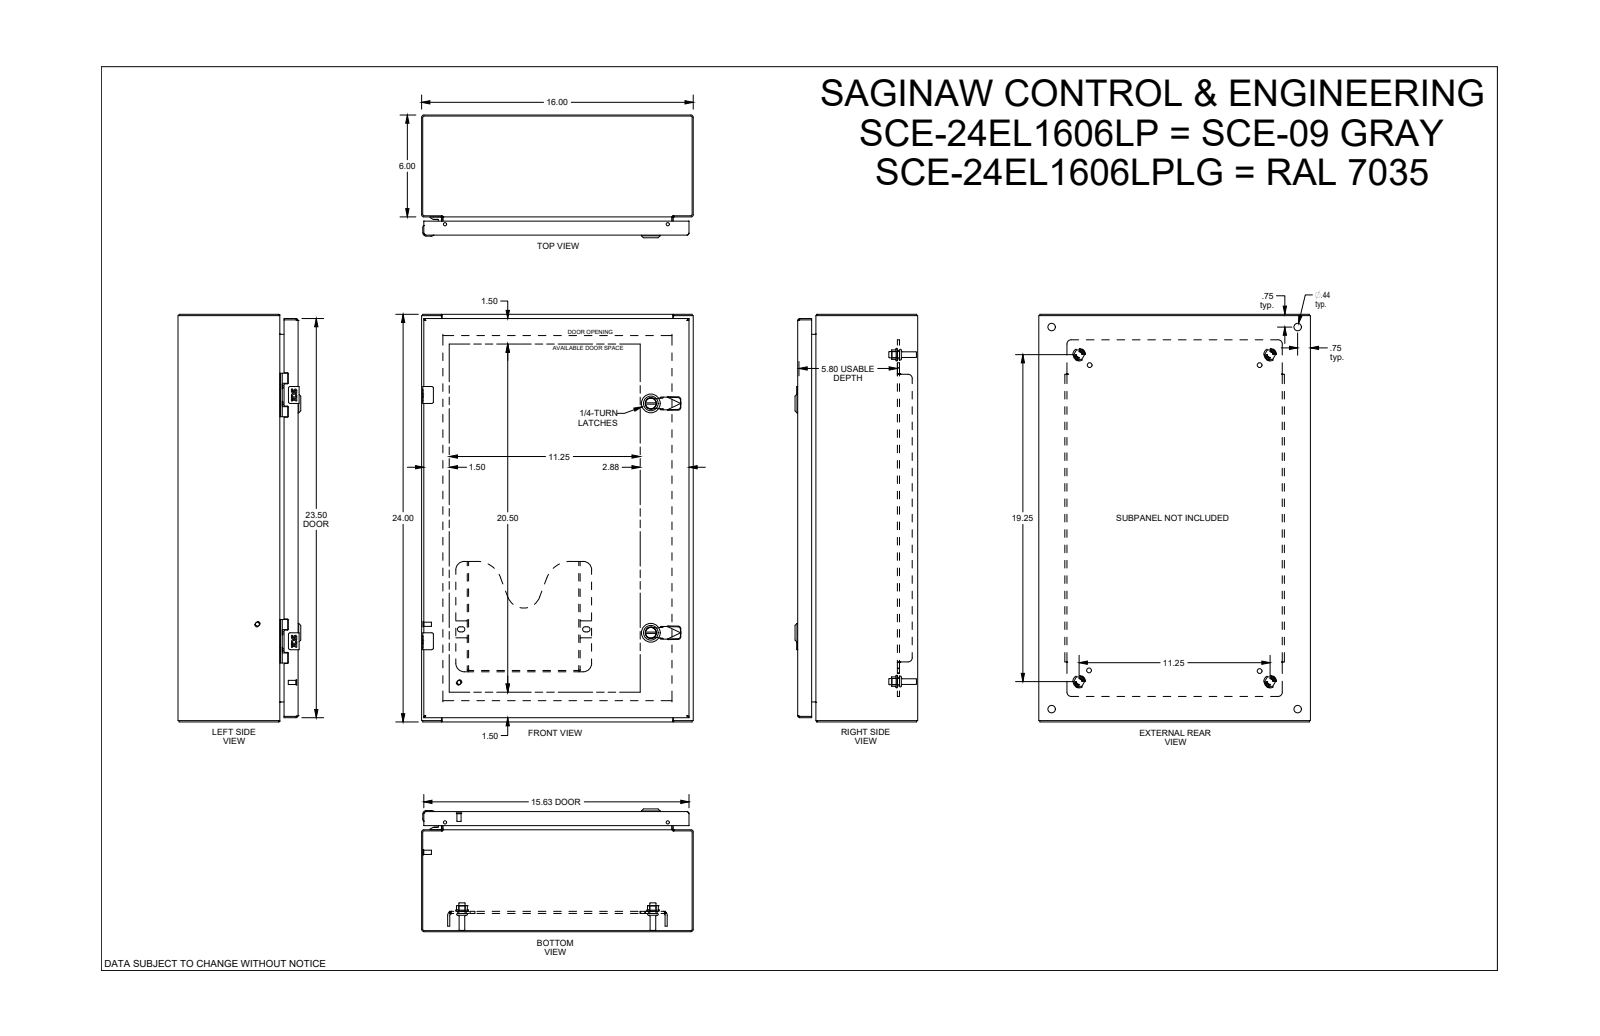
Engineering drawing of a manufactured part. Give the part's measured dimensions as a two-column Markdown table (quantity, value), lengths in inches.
| quantity | value |
| --- | --- |
| part name | SCE-24EL1606LP |
| STEP written by | SolidWorks 2021 (AUTOMOTIVE_DESIGN) |
| units | inches |
| bodies | 45 solids, 2787 faces (1089 planar, 840 cylindrical, 858 other) |
| overall size | 24 × 16 × 7.23 |
| volume | 156.9 in³ |
| surface area | 3 771 in² |
| round holes (diameter × count) | 0.172 × 4, 0.205 × 4, 0.244 × 4, 0.266 × 4, 0.281 × 4, 0.367 × 4, 0.375 × 4, 0.437 × 4, 0.5 × 4, 0.04 × 2, 0.188 × 2, 0.197 × 2 |
| round bosses / shafts (diameter × count) | 0.17 × 6, 0.366 × 4, 0.332 × 4, 0.25 × 4, 0.248 × 4, 0.24 × 4, 0.196 × 3, 1.102 × 2 |
| partial cylindrical surfaces (radius × count) | 0.012 × 56, 0.01 × 28, 0.015 × 24, 0.02 × 20, 0.04 × 17, 0.06 × 13, 0.029 × 12, 0.1 × 12 |
| main face-to-face distances | 0.075, 0.06, 7.073, 6.998, 7.013, 6.938, 1, 0.125, 15.925, 1.2 |
| hole center spacings | 14.5, 0.985, 0.02, 0.493, 0.494, 2.298, 4.493, 12.978 |
